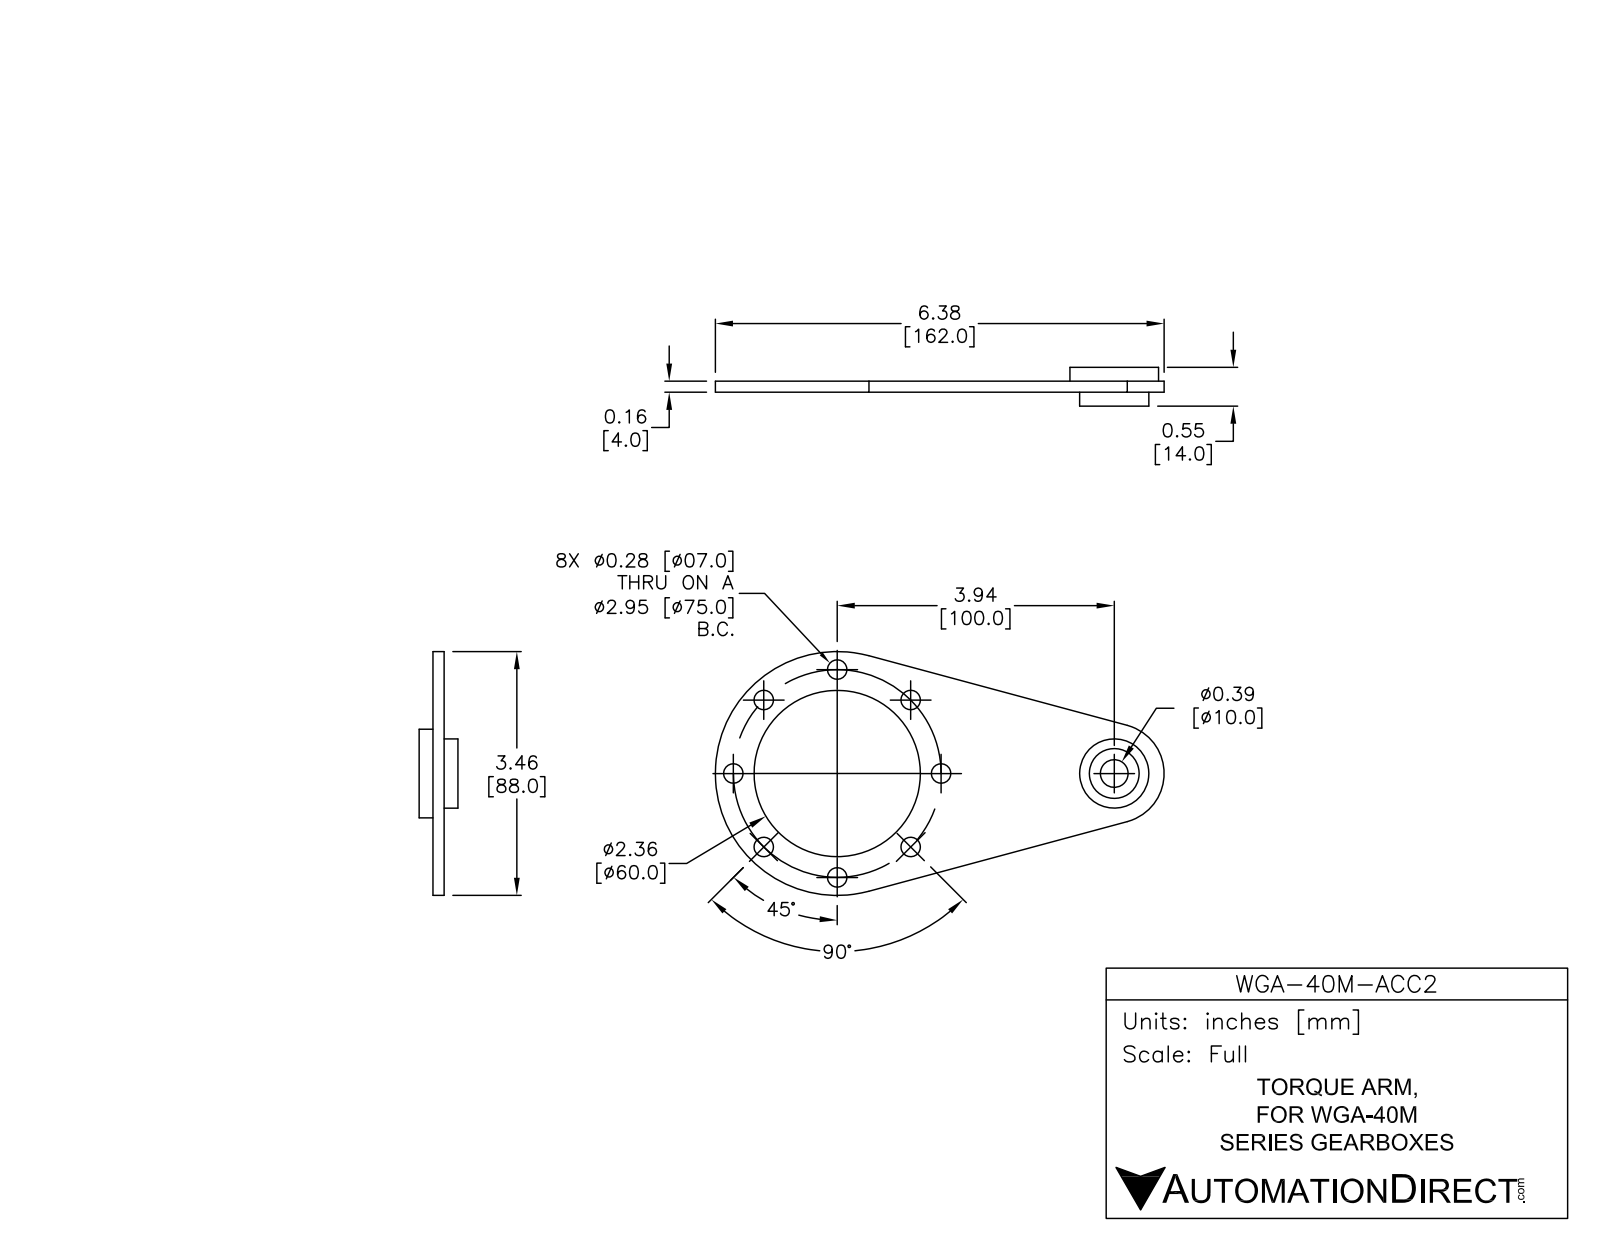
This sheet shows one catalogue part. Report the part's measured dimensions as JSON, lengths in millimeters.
{"part_name": "WGA-40M-ACC2", "step_written_by": "SolidWorks 2014 (AUTOMOTIVE_DESIGN)", "units": "millimeters", "bodies": {"solids": 2, "faces": 40, "planar": 8, "cylindrical": 32, "other": 0}, "overall_size": [162, 88, 14], "volume_mm3": 32680, "surface_area_mm2": 19480, "round_holes": [[7, 8], [10, 1], [18, 1], [60, 1]], "round_bosses_or_shafts": [[32, 1], [25, 1]], "partial_cylinders_radius": [[18, 1], [44, 1]], "face_to_face_distances": [4, 5, 9, 14], "hole_center_spacings": [28.7, 37.5, 69.3, 53, 53, 75, 75, 78.1]}
